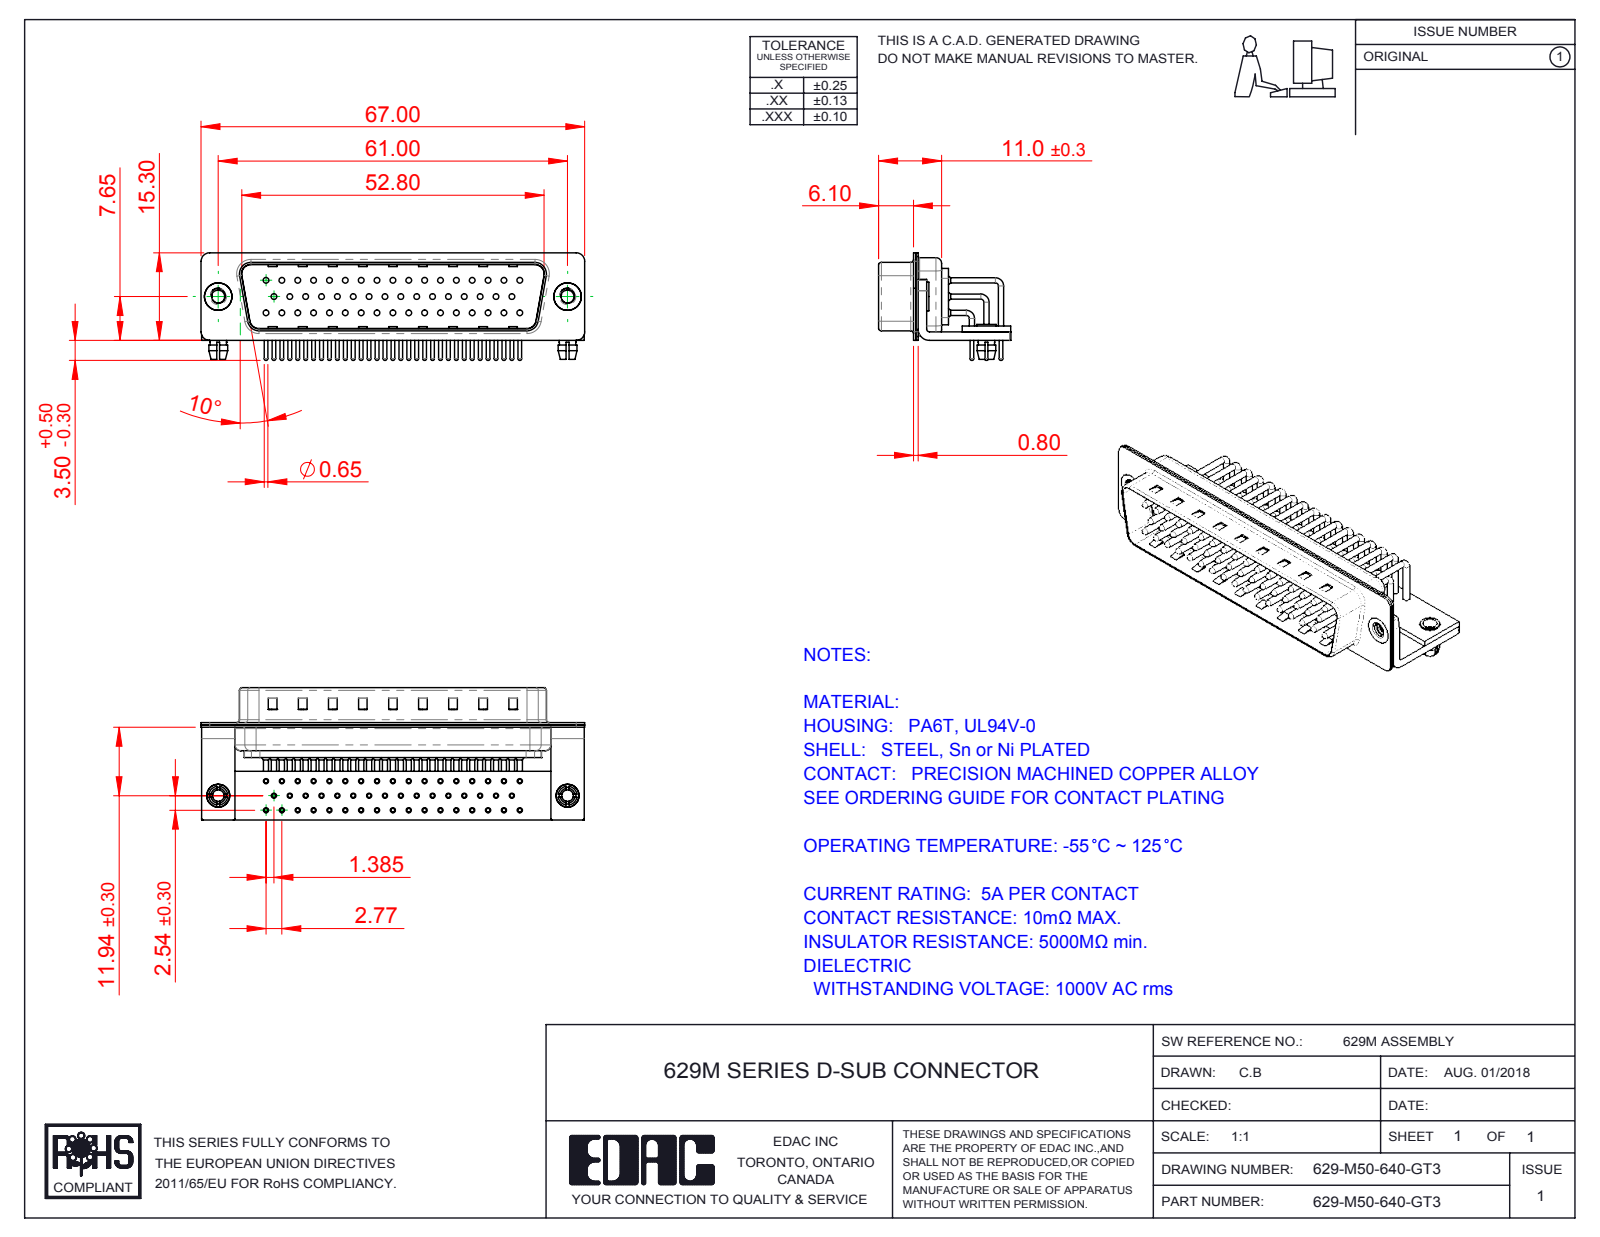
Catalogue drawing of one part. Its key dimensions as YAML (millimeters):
part_name: "629M Stabilizer Board_50 Contacts; 629M Board Lock_50 Contacts; 629M Contact Row 3; 629-M50-640-GT3 (+7 more)"
step_written_by: "SolidWorks 2016 (CONFIG_CONTROL_DESIGN)"
units: millimeters
bodies: {solids: 60, faces: 6154, planar: 3477, cylindrical: 2095, other: 582}
overall_size: [67, 23.1, 18.8]
volume: 5879
surface_area: 15169
round_holes:
  - {diameter: 2, count: 52}
  - {diameter: 0.9, count: 50}
  - {diameter: 1, count: 50}
  - {diameter: 1.7, count: 50}
  - {diameter: 2.26, count: 2}
  - {diameter: 2.5, count: 2}
  - {diameter: 3.2, count: 2}
  - {diameter: 4, count: 2}
  - {diameter: 4.8, count: 2}
round_bosses_or_shafts:
  - {diameter: 0.9, count: 58}
  - {diameter: 1.5, count: 50}
  - {diameter: 0.65, count: 50}
  - {diameter: 5, count: 2}
  - {diameter: 4.9, count: 2}
  - {diameter: 4, count: 2}
  - {diameter: 3.4, count: 2}
  - {diameter: 3.3, count: 2}
partial_cylinders:
  - {radius: 1.01, count: 50}
  - {radius: 0.25, count: 16}
  - {radius: 1.5, count: 16}
  - {radius: 2, count: 13}
  - {radius: 0.5, count: 9}
  - {radius: 1.6, count: 8}
  - {radius: 0.6, count: 4}
  - {radius: 0.65, count: 4}
face_to_face_distances: [0.4, 1, 11.55, 1.5, 0.83, 5.7, 0.43, 11.95, 1.9, 0.8]
hole_center_spacings: [2.77, 5.54, 8.31, 11.08, 13.85, 16.62, 3.16, 19.39]
